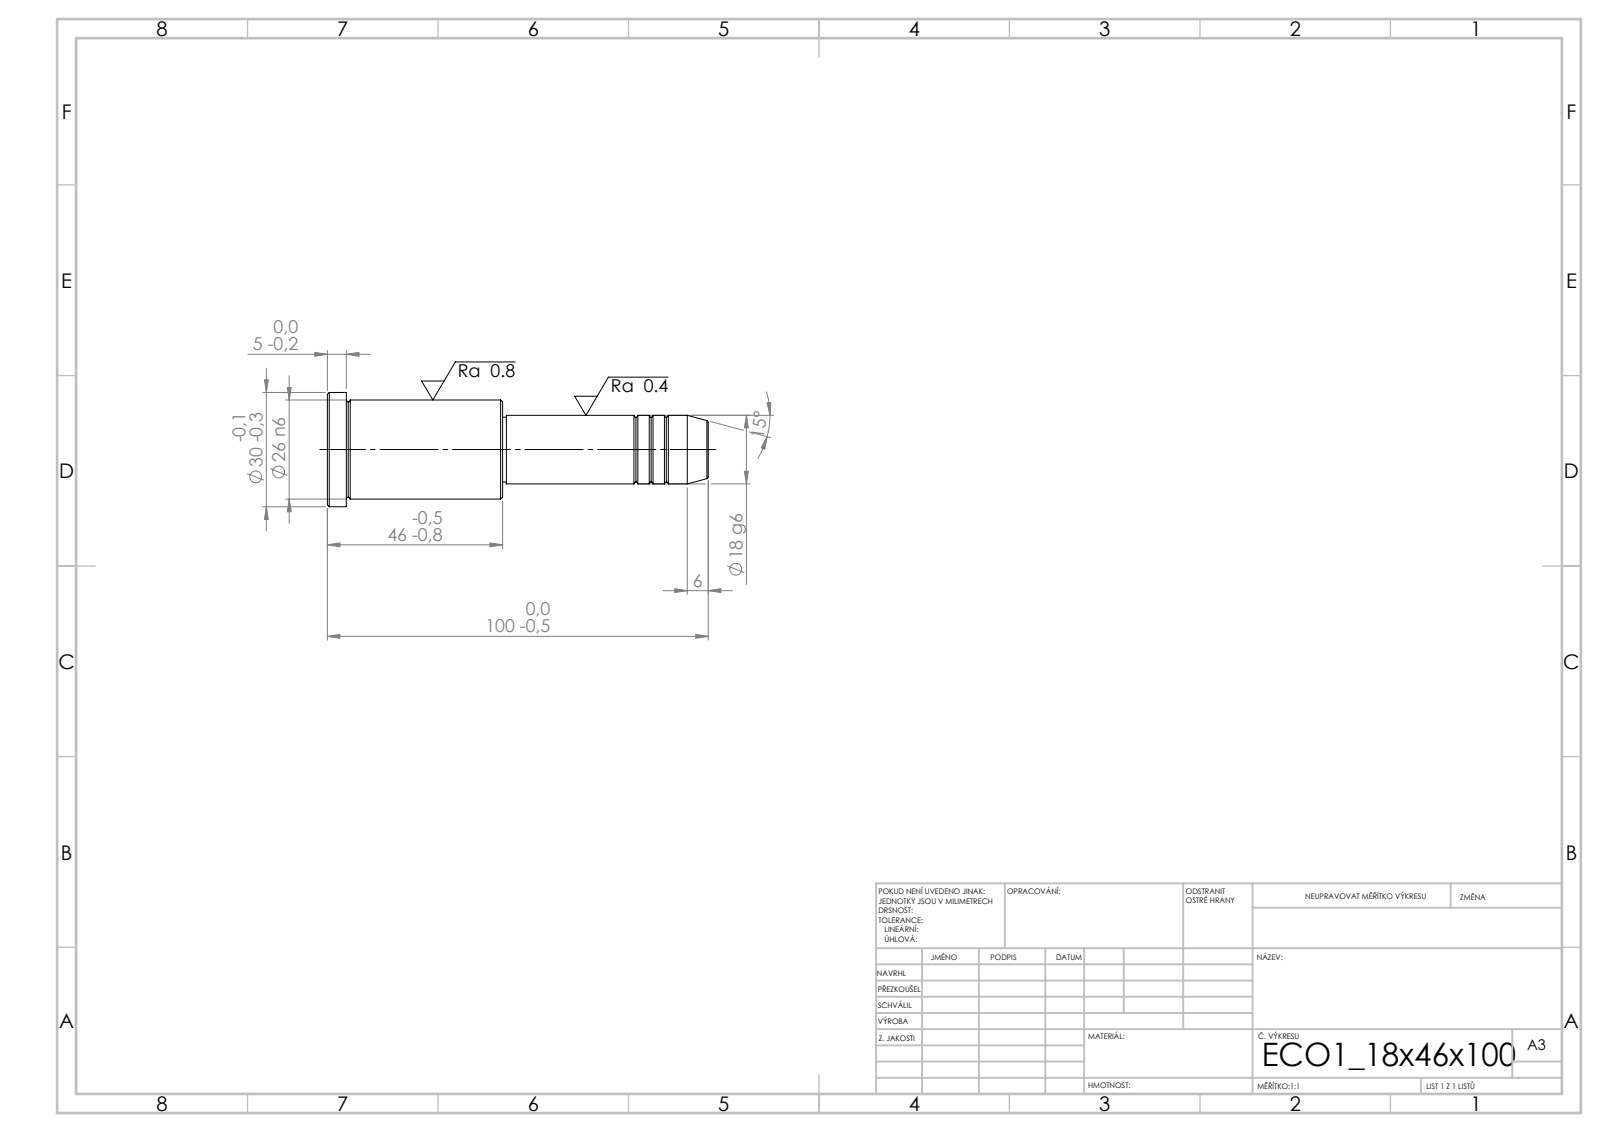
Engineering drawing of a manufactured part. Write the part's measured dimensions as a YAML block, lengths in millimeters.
step_written_by: "SolidWorks 2019 (CONFIG_CONTROL_DESIGN)"
units: millimeters
bodies: {solids: 1, faces: 43, planar: 5, cylindrical: 14, other: 24}
overall_size: [100, 30, 30]
volume: 38680
surface_area: 8321
round_bosses_or_shafts:
  - {diameter: 30, count: 1}
  - {diameter: 26, count: 1}
  - {diameter: 18, count: 1}
  - {diameter: 17, count: 1}
face_to_face_distances: [46, 41, 5, 54, 95, 100, 53, 1, 42, 47]
